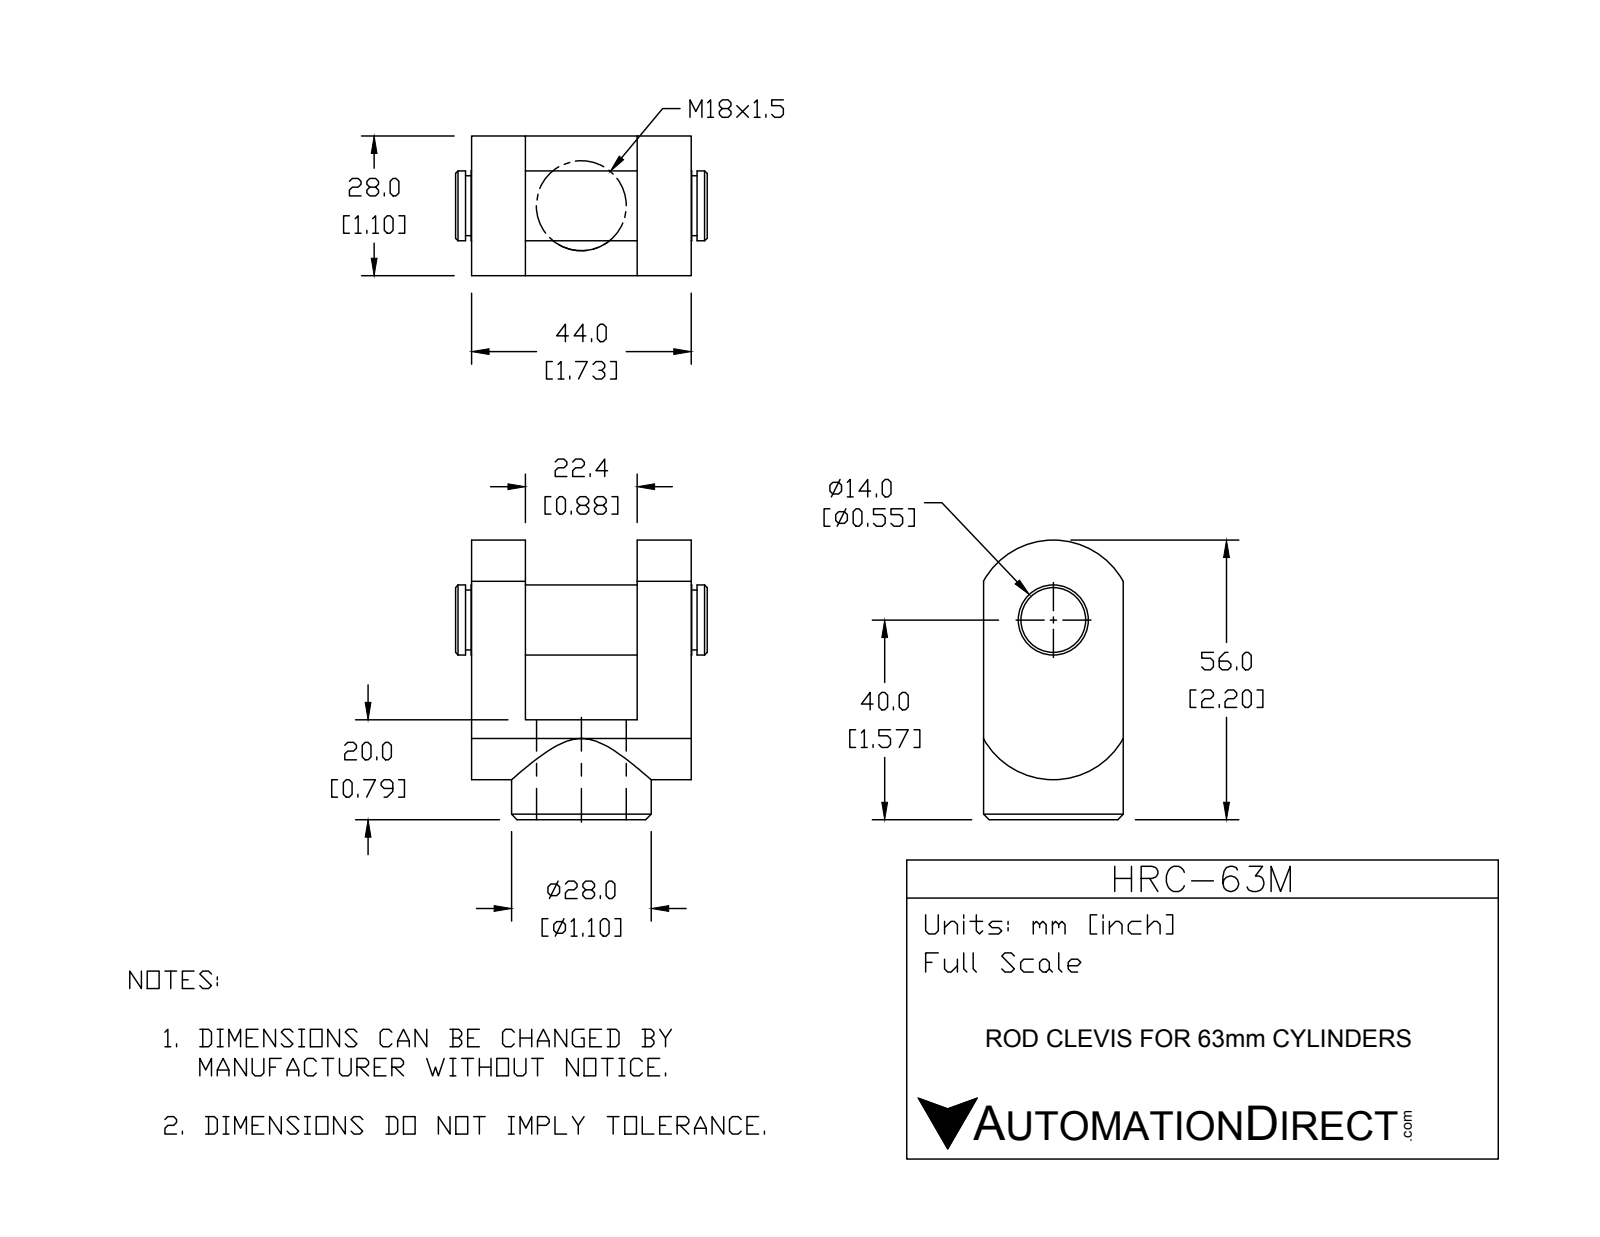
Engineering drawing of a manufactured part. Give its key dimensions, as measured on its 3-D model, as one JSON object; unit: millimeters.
{"part_name": "HRC-63M", "step_written_by": "SolidWorks 2015 (CONFIG_CONTROL_DESIGN)", "units": "millimeters", "bodies": {"solids": 2, "faces": 46, "planar": 14, "cylindrical": 22, "other": 10}, "overall_size": [56, 50.4, 28], "volume_mm3": 38140, "surface_area_mm2": 13128, "round_holes": [[16.5, 1]], "round_bosses_or_shafts": [[28, 1], [14, 1], [12, 1]], "partial_cylinders_radius": [[16, 2]], "face_to_face_distances": [10.8, 33.2, 44, 22.4, 28, 20, 3.2, 14, 36.4, 47.2]}
